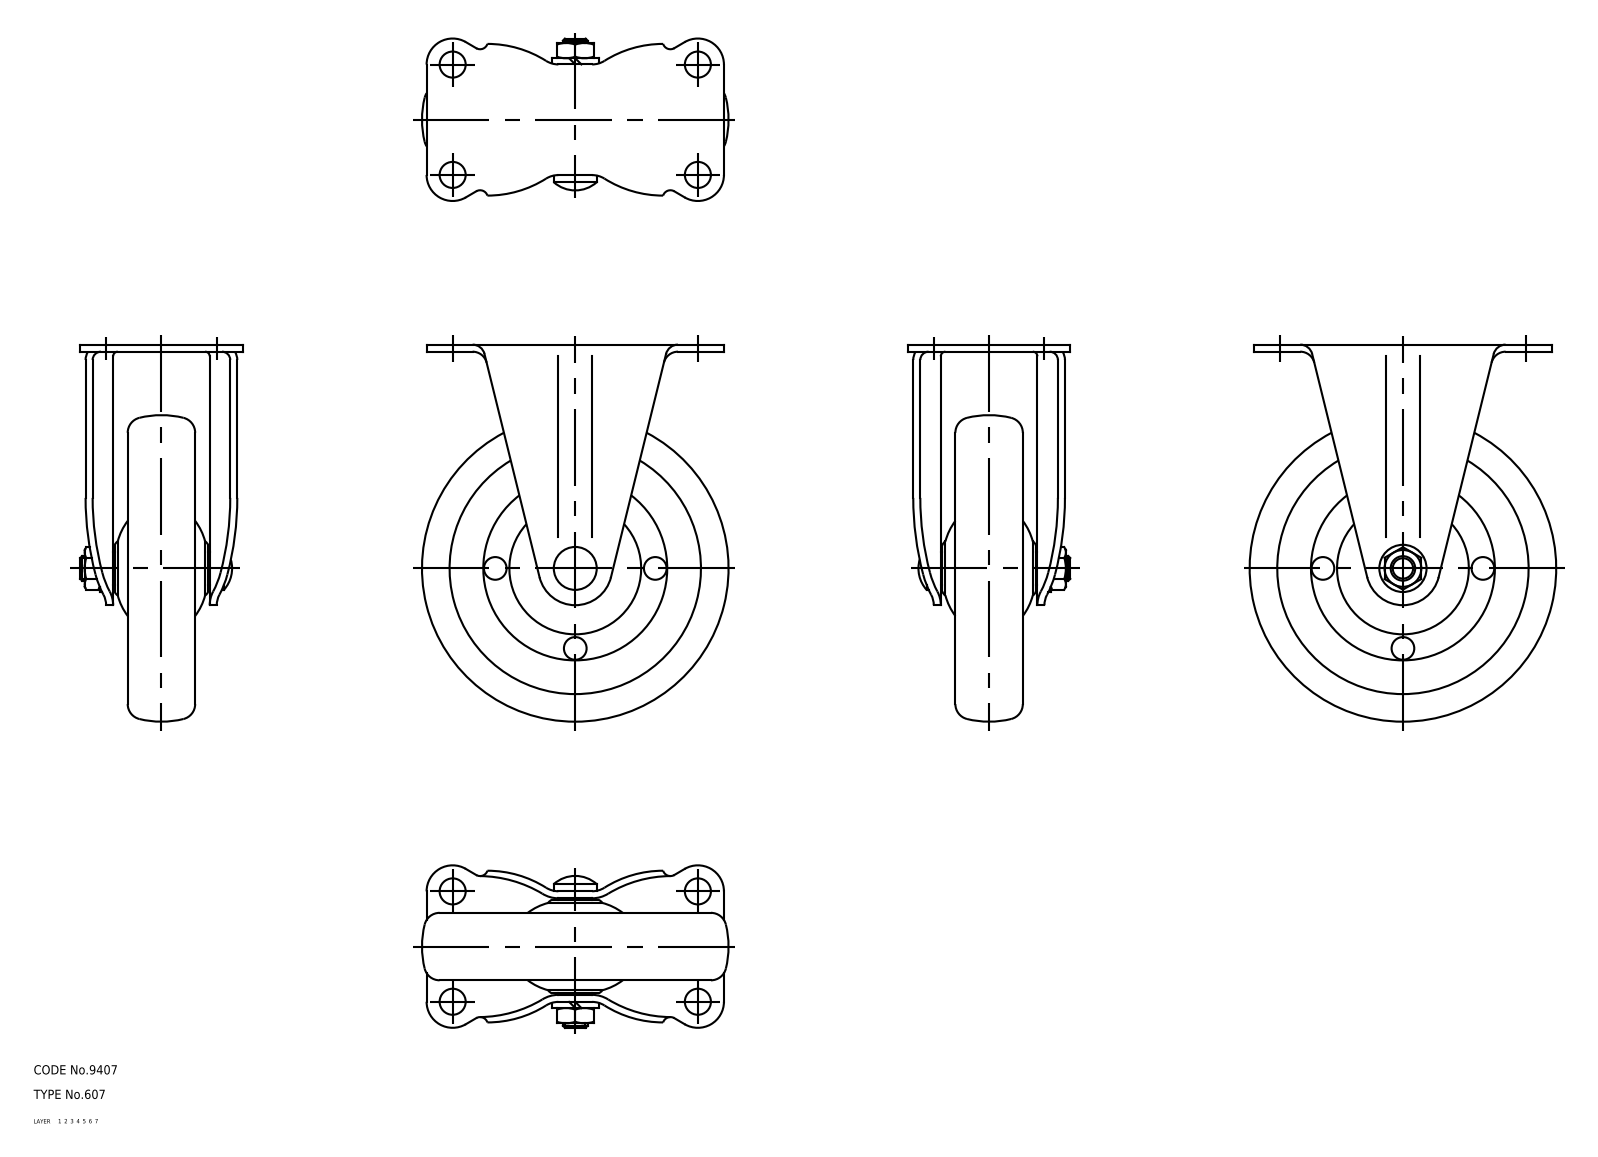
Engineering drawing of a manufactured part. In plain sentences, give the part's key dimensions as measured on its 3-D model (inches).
The part is named "wheel; axle; No_607_17102_36". Its 3-D file was written by "CADfix (AUTOMOTIVE_DESIGN)". It is 3 solids with 176 faces: 0 planar, 0 cylindrical and 176 other. Overall it measures 4.843 by 3.937 by 2.087 inches. Its volume is 10.4 cubic inches and its surface area 74.29 square inches.
